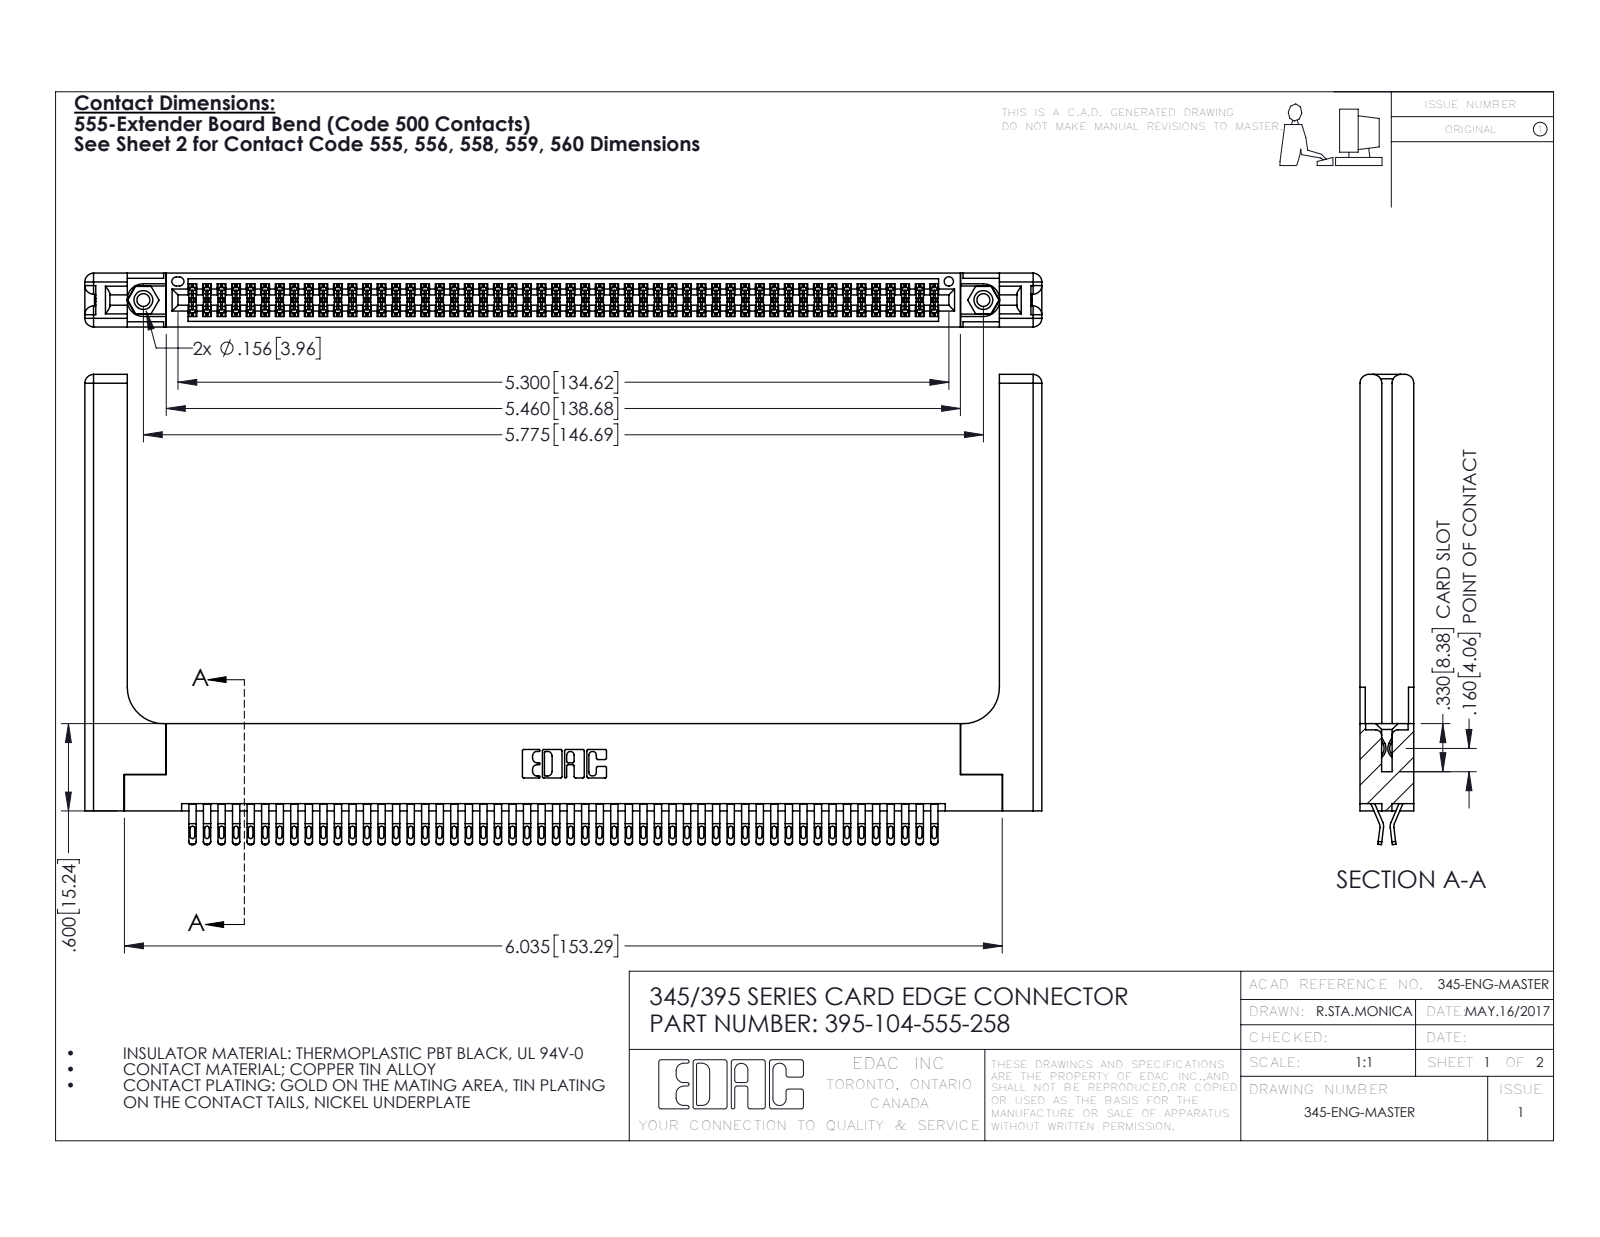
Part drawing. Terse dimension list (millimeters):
name: 345-292-001_555 Tail; 395-104-555-258; 345-250-001_345-250-001-102; 345-220-058_345-220-058 (+1 more)
written by: SolidWorks 2016 (CONFIG_CONTROL_DESIGN)
unit: mm
bodies: 109 solids, 6206 faces (3452 planar, 2694 cylindrical, 60 other)
size: 167.1 × 82.1 × 9.4
volume: 25 100 mm³; area: 30 880 mm²
holes: 2× ⌀2.3, 2× ⌀3.2, 2× ⌀4, 1× ⌀1.6
bosses: 2× ⌀3.9
rounds: 260× R0.4, 208× R0.5, 156× R0.2, 22× R0.3, 16× R1.5, 6× R0.2, 6× R0.8, 3× R0.7
face distances: 1.8, 7.6, 9.4, 0.6, 5.1, 2.5, 6.9, 5.7, 3.8, 3.8
hole spacings: 6.9, 140.7, 146.7
